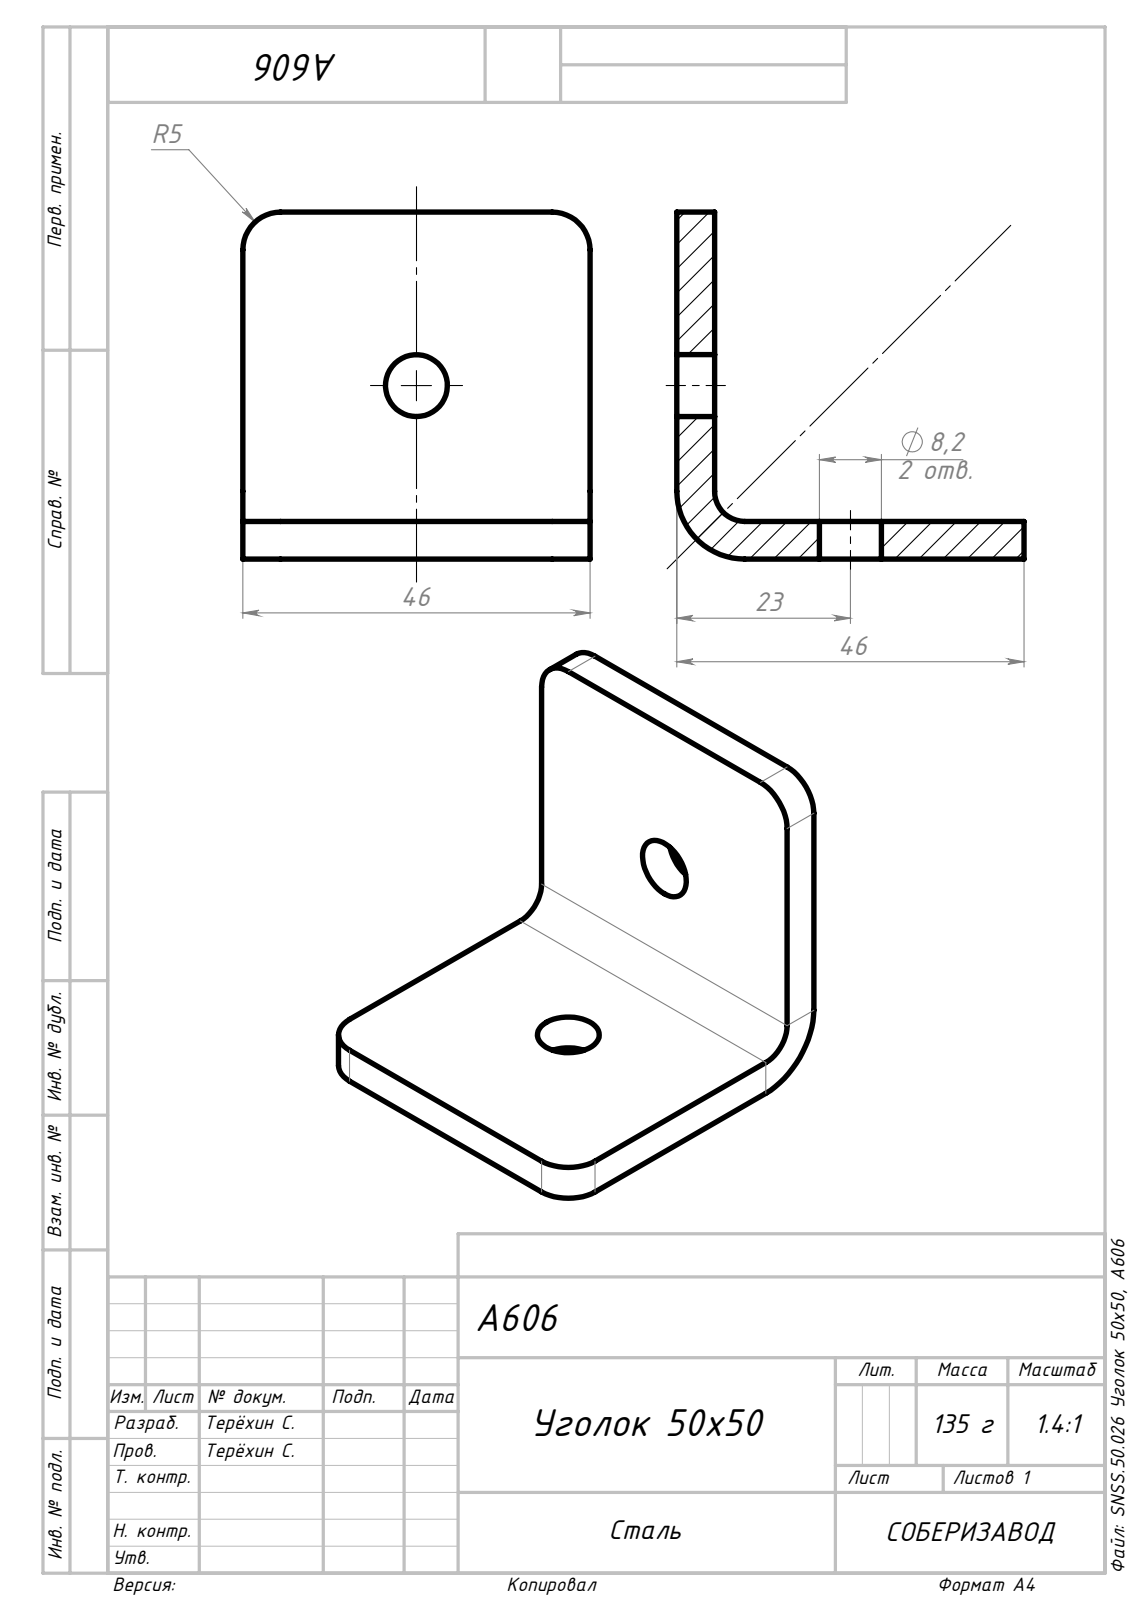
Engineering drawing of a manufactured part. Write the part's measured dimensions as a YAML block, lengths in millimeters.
part_name: "SNSS.50.026 Уголок 50х50, A606"
step_written_by: "SolidWorks 2021 (AUTOMOTIVE_DESIGN)"
units: millimeters
bodies: {solids: 1, faces: 22, planar: 12, cylindrical: 10, other: 0}
overall_size: [46, 46, 46]
volume: 18733
surface_area: 9010
round_holes:
  - {diameter: 8.2, count: 2}
partial_cylinders:
  - {radius: 5, count: 4}
  - {radius: 4, count: 1}
  - {radius: 9, count: 1}
face_to_face_distances: [5, 46, 41]
